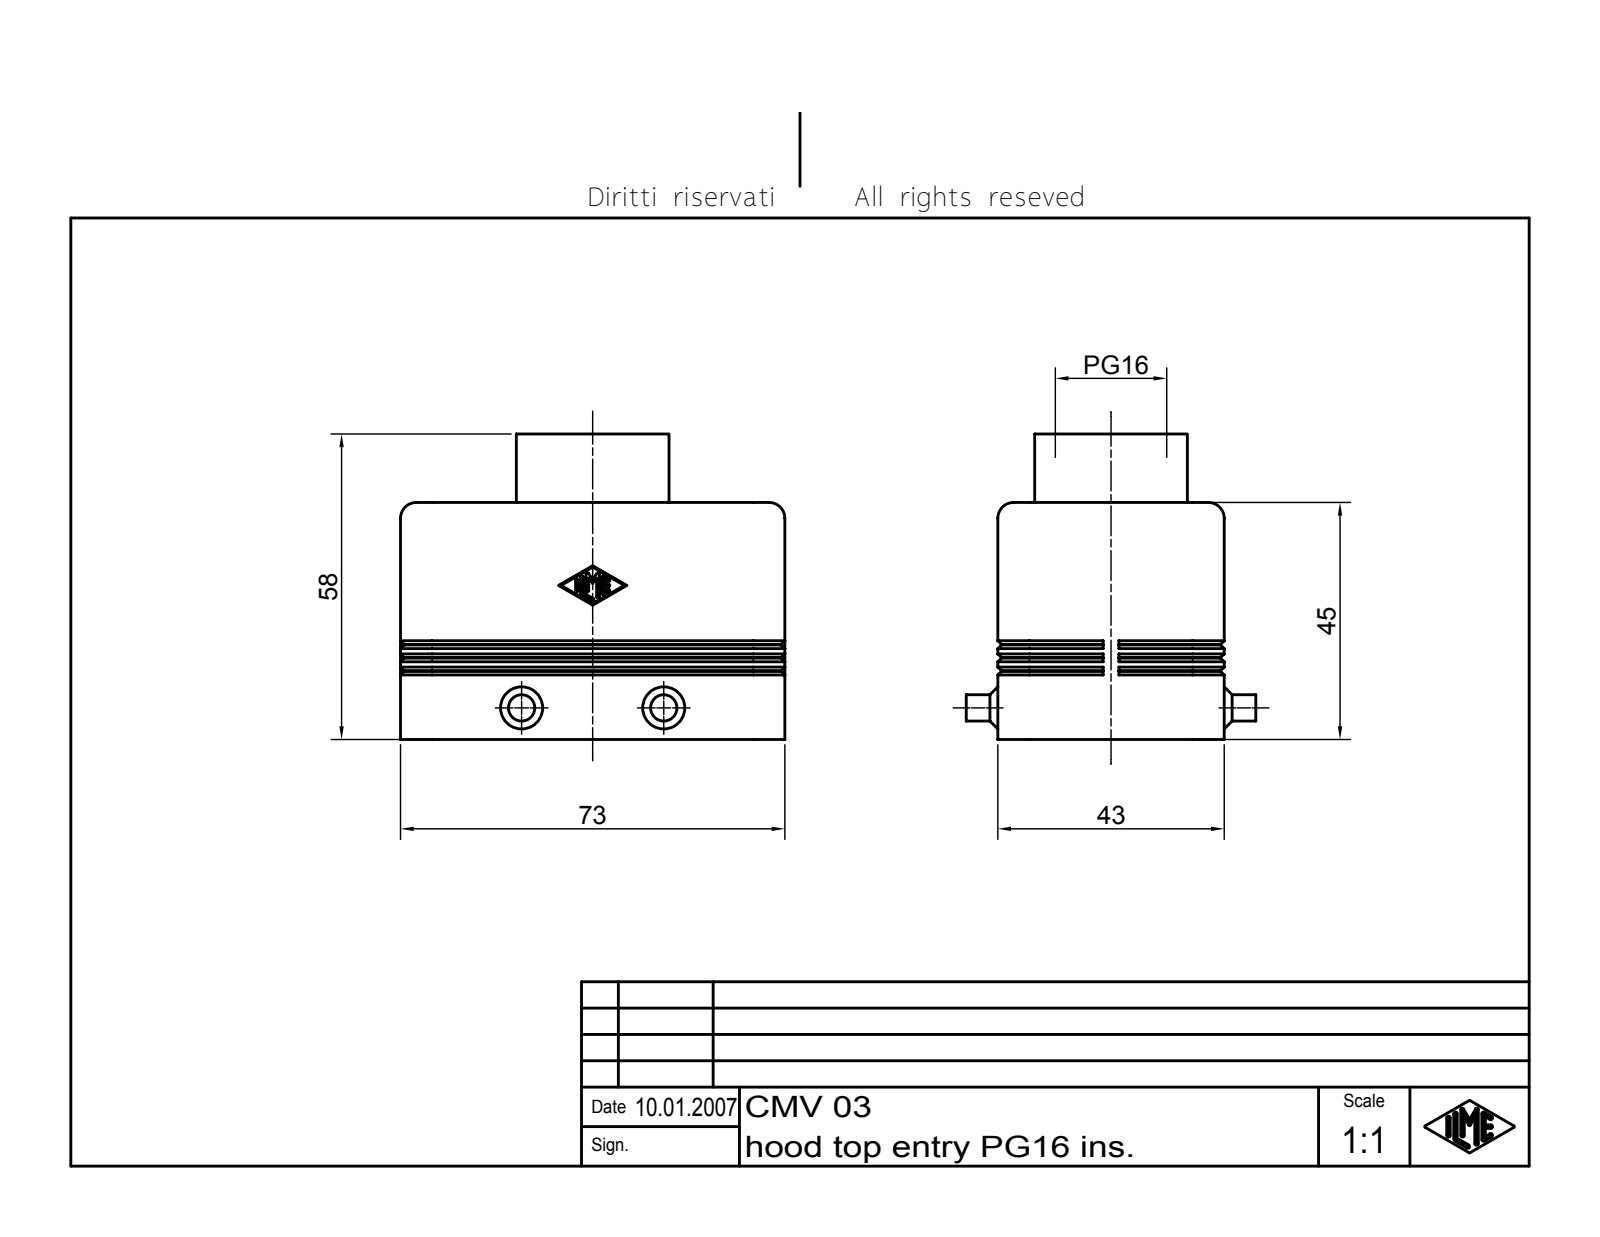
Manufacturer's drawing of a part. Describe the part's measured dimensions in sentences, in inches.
The part is named "CHV Tüllengehäuse 2 Bügel für einen Einsatz". Its 3-D file was written by "Autodesk Inventor 7 (AUTOMOTIVE_DESIGN)". It is 1 solid with 332 faces: 124 planar, 83 cylindrical and 125 other. Overall it measures 2.874 by 2.283 by 2.165 inches. Its volume is 2.974 cubic inches and its surface area 42.88 square inches. Round holes: 1 of diameter 0.63, 1 of diameter 0.833. Round bosses or shafts: 2 of diameter 0.197, 1 of diameter 1.142. Partial cylindrical surfaces (rounded edges, fillets, slot ends): 14 of radius 0.01, 8 of radius 0.118, 4 of radius 0.079, 4 of radius 0.236, 2 of radius 0.209, 1 of radius 0.059. The main face-to-face distances are 0.118, 1.575, 1.457, 1.693, 0.453, 0.335, 2.756, 2.874, 2.638, 1.122.
